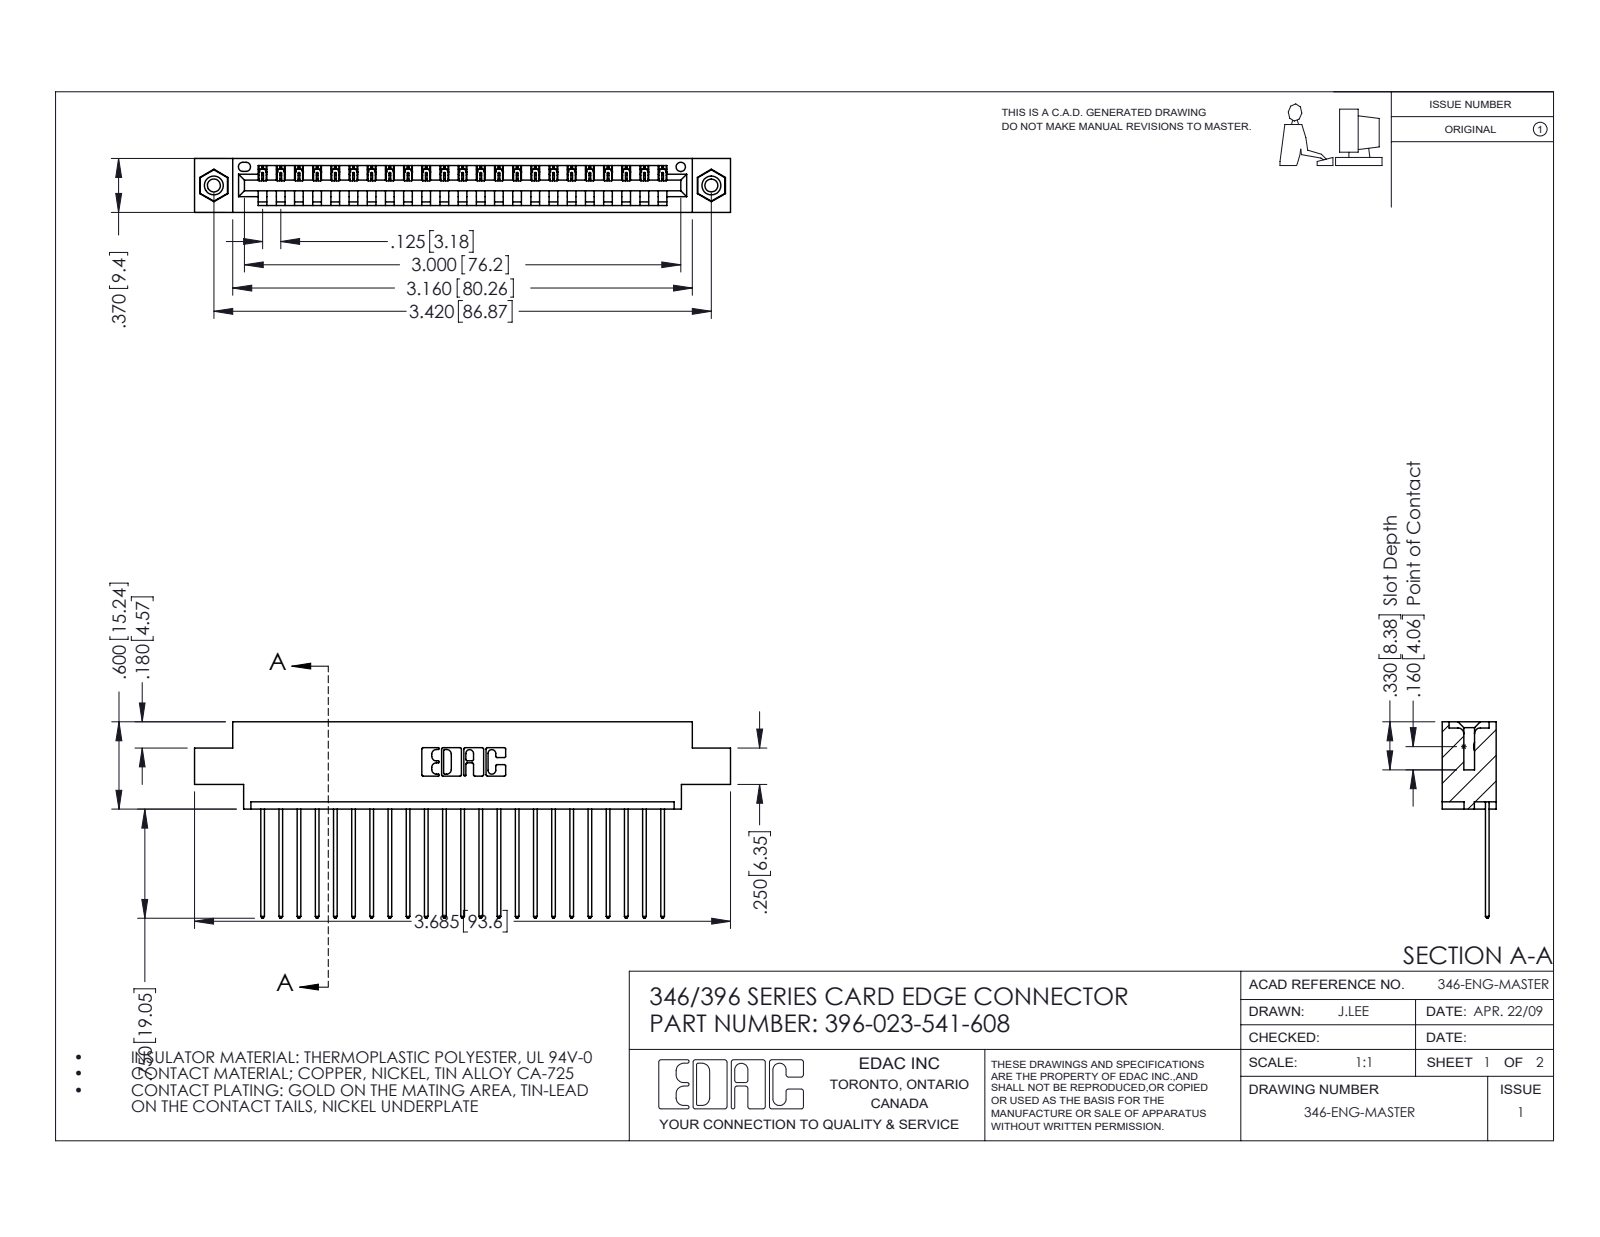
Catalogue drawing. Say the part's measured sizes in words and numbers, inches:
The part is named "396-023-541-608; 345-292-001_345-293-141; 345-250-001_345-250-003-102; 346 Part_0.170 Offset - 0.156 Dia-TI". Its 3-D file was written by "SolidWorks 2016 (CONFIG_CONTROL_DESIGN)". It is 26 solids with 1520 faces: 1032 planar, 472 cylindrical and 16 other. Overall it measures 3.685 by 1.35 by 0.37 inches. Its volume is 0.534 cubic inches and its surface area 17.61 square inches. Round holes: 2 of diameter 0.089, 2 of diameter 0.125, 2 of diameter 0.156, 1 of diameter 0.064. Round bosses or shafts: 2 of diameter 0.155. Partial cylindrical surfaces (rounded edges, fillets, slot ends): 46 of radius 0.006, 46 of radius 0.01, 22 of radius 0.01, 6 of radius 0.007, 6 of radius 0.031, 3 of radius 0.026, 2 of radius 0.031, 2 of radius 0.04. The main face-to-face distances are 0.048, 0.322, 0.37, 0.25, 0.072, 0.298, 0.025, 0.222, 0.148, 0.1. The hole center spacings are 0.246, 3.212, 3.42.
